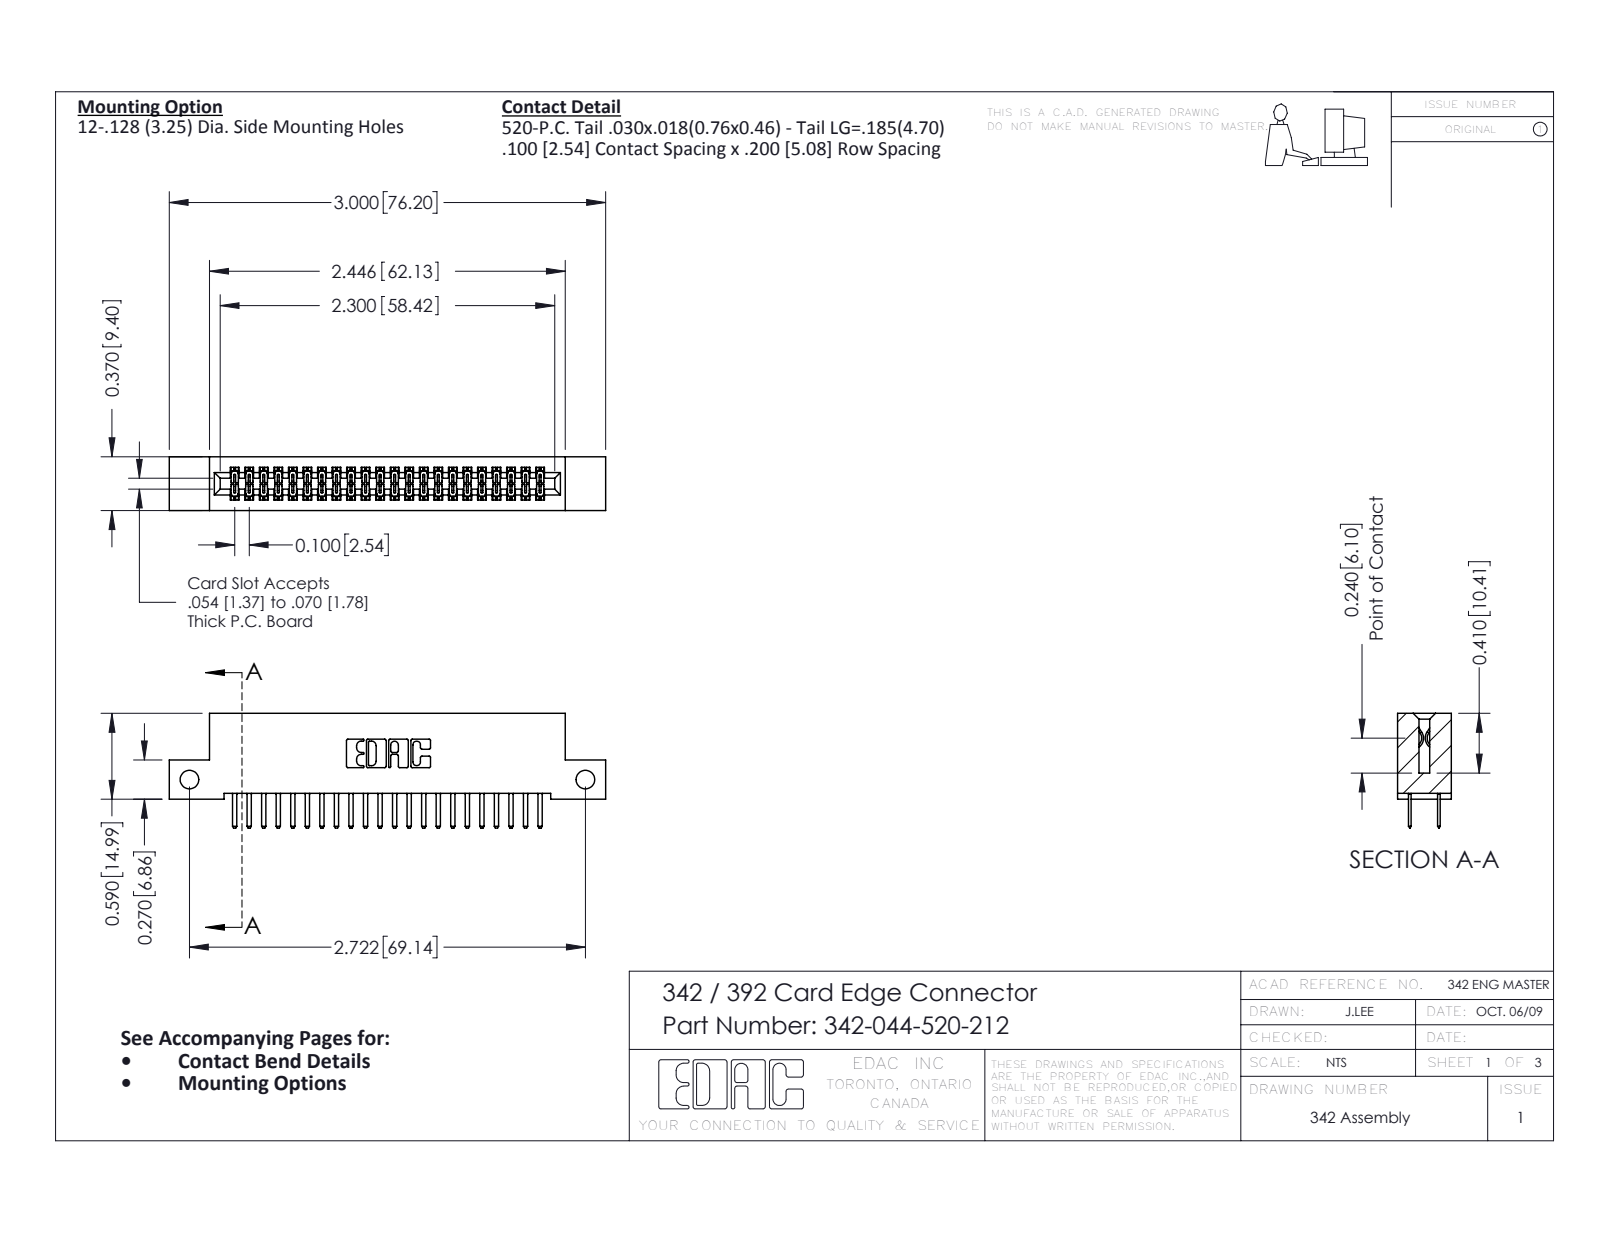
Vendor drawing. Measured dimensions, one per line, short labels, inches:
name: 342 Part_Side Mount; 345-292-001_345-293-120; 342-044-520-212
written by: SolidWorks 2016 (CONFIG_CONTROL_DESIGN)
unit: in
bodies: 45 solids, 2574 faces (1738 planar, 836 cylindrical, 0 other)
size: 3 × 0.788 × 0.37
volume: 0.406 in³; area: 15.72 in²
holes: 2× ⌀0.128
rounds: 92× R0.01, 66× R0.006, 22× R0.01, 6× R0.007, 6× R0.031, 3× R0.026, 2× R0.014, 2× R0.022
face distances: 0.072, 0.298, 0.37, 0.2, 0.225, 0.076, 0.148, 0.222, 0.15, 0.022
hole spacings: 2.722
